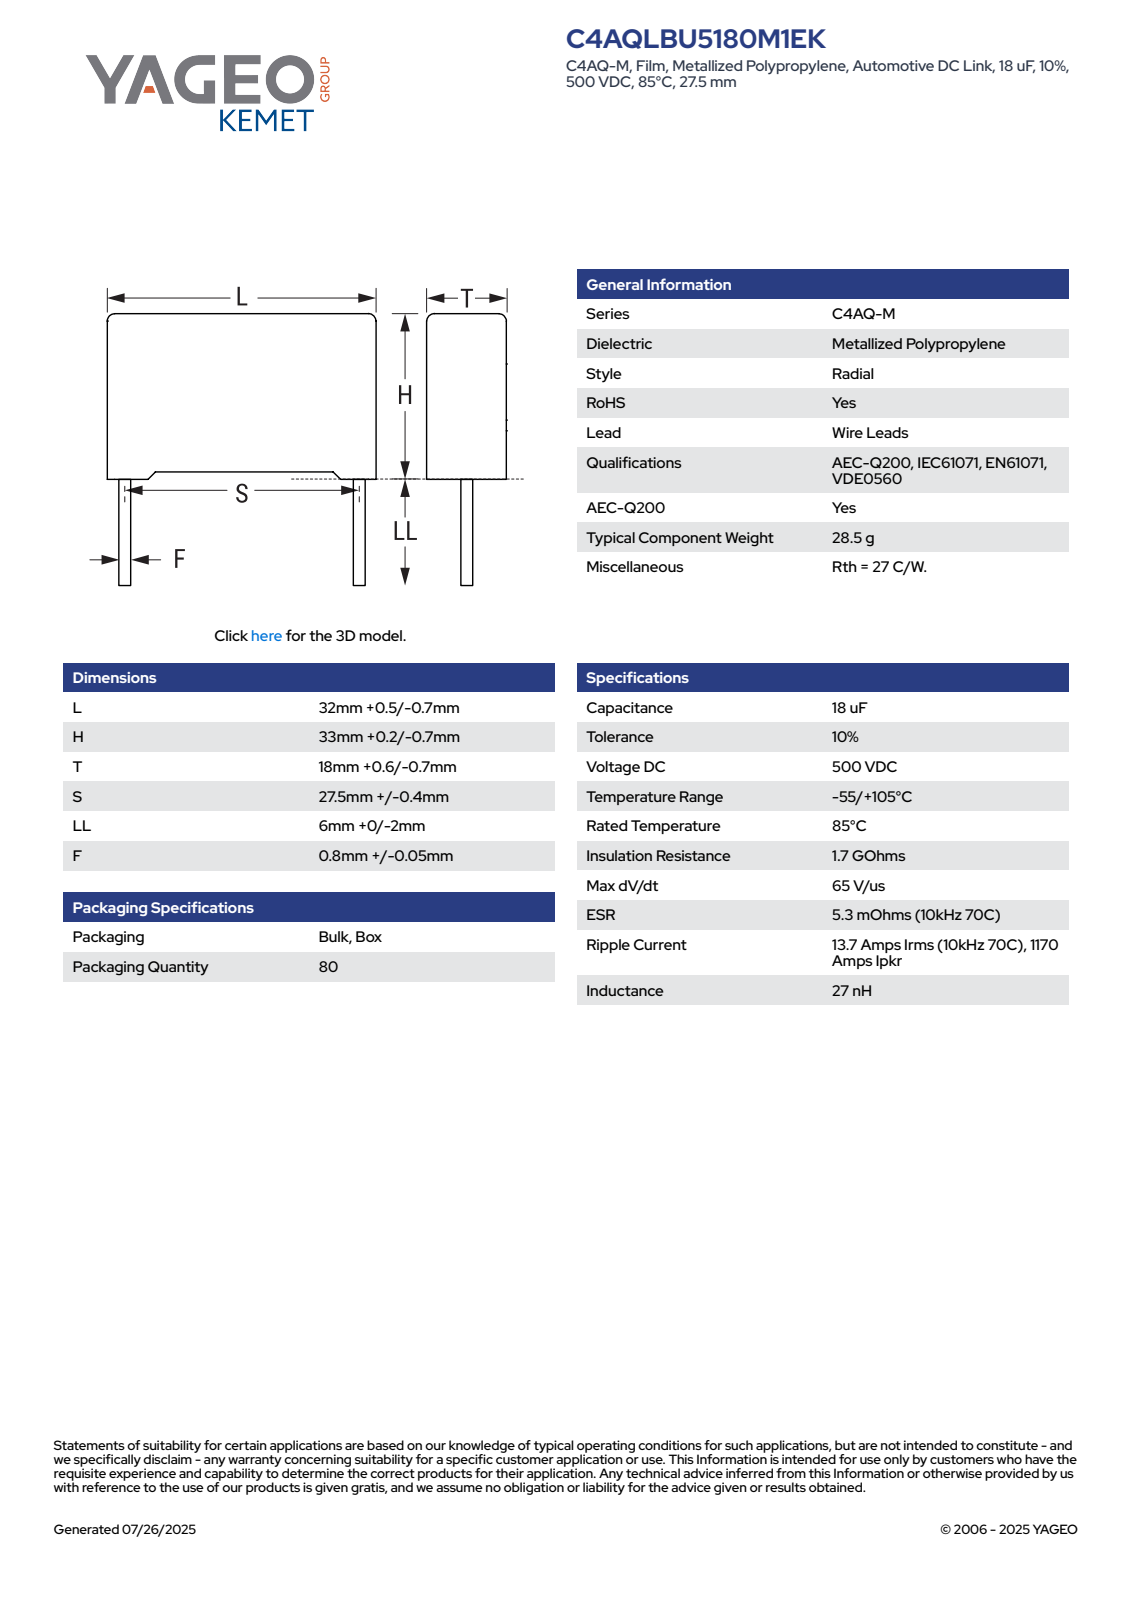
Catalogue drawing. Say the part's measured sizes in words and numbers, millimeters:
The part is named "CFR_RB2CFP_32X33X18_L32.5H33.2T18.6S27.5LL6F0.85". Its 3-D file was written by "SolidWorks 2014 (AUTOMOTIVE_DESIGN)". It is 4 solids with 85 faces: 77 planar, 8 cylindrical and 0 other. Overall it measures 39.2 by 32.5 by 18.61 millimeters. Its volume is 19 490 cubic millimeters and its surface area 4 684 square millimeters. Round bosses or shafts: 2 of diameter 0.85. Partial cylindrical surfaces (rounded edges, fillets, slot ends): 4 of radius 0.5. The main face-to-face distances are 18.6, 32.5, 32.06, 0.39, 32.45, 0.75, 1.14, 33.2, 1.08, 31.42.
